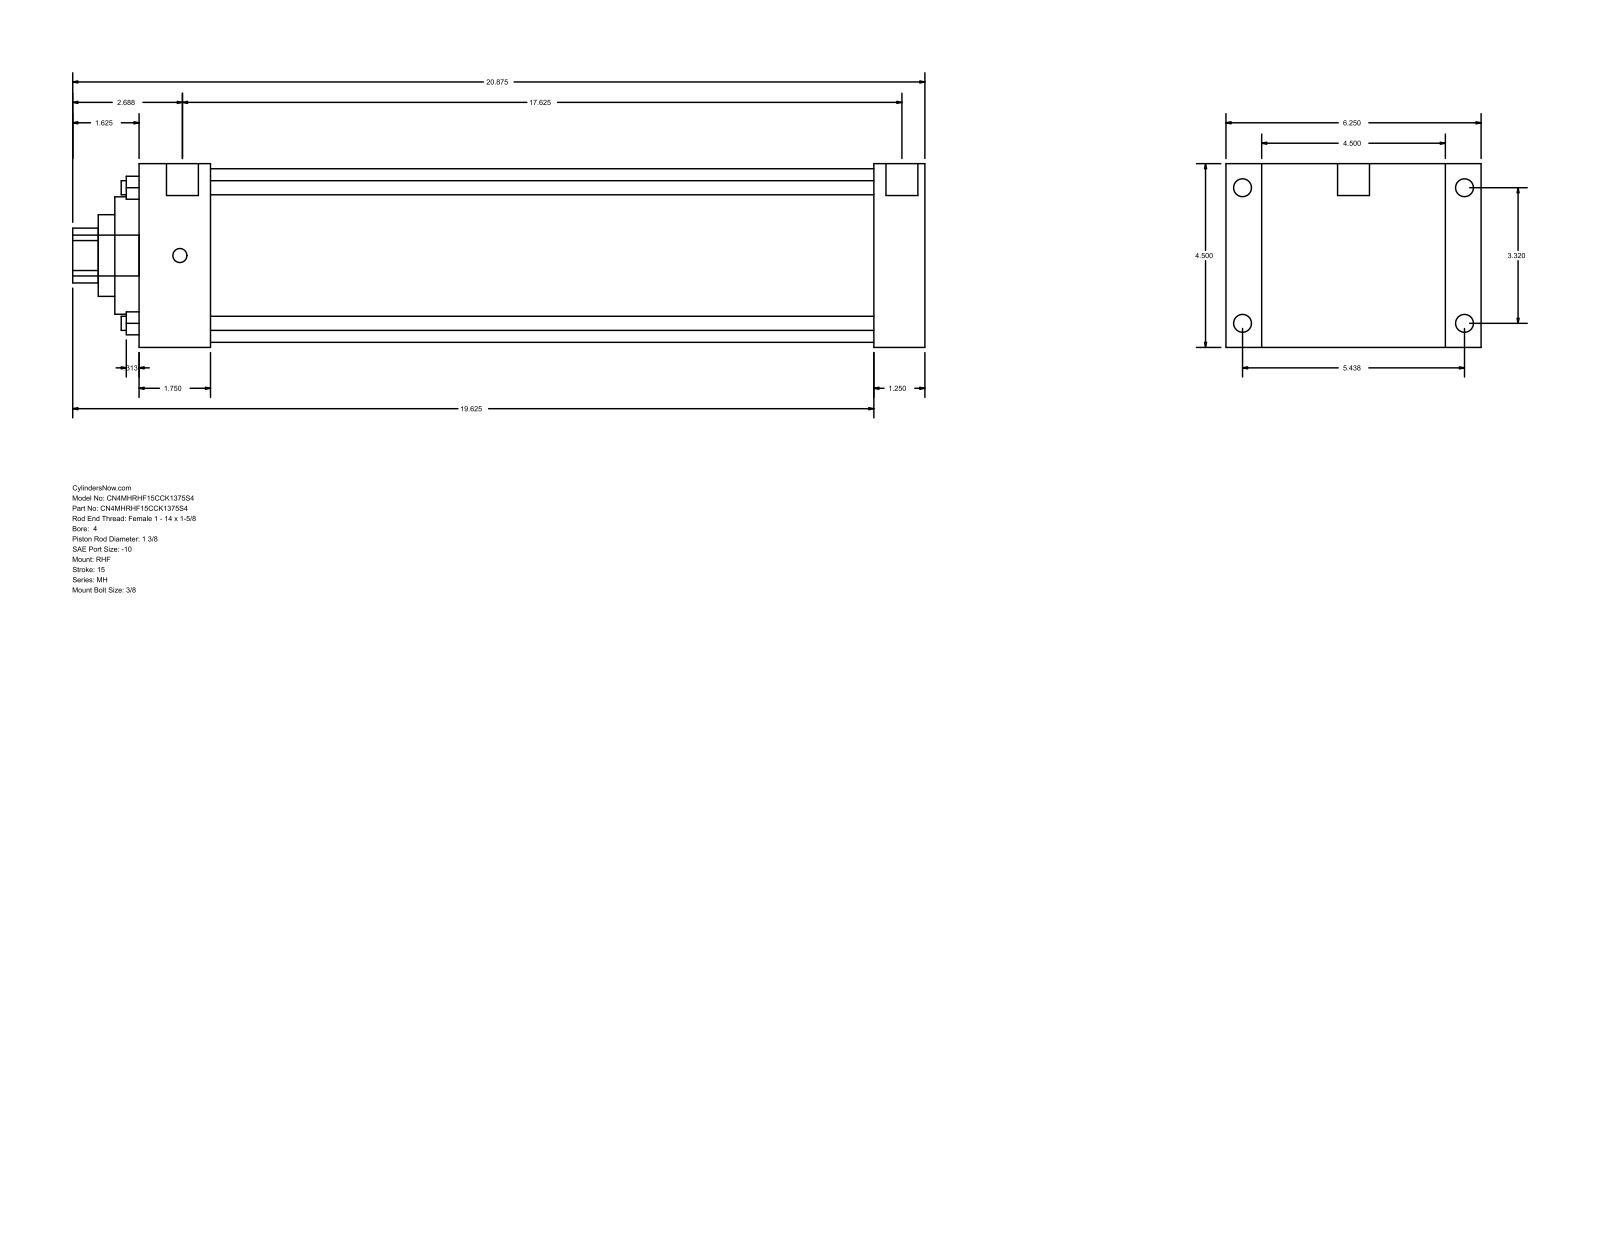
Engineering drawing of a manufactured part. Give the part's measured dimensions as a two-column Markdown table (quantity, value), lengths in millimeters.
| quantity | value |
| --- | --- |
| part name | MH_RHF__0400_1.375 |
| STEP written by | GSSL Pune (CONFIG_CONTROL_DESIGN) |
| units | millimeters |
| bodies | 0 solids, 90 faces (61 planar, 29 cylindrical, 0 other) |
| overall size | 530.23 × 158.75 × 114.3 |
| round holes (diameter × count) | 8.76 × 4, 34.92 × 1, 50.8 × 1, 73.03 × 1, 107.95 × 1 |
| round bosses / shafts (diameter × count) | 11.13 × 4, 8.73 × 4, 19.84 × 2, 25.4 × 1 |
| partial cylindrical surfaces (radius × count) | 17.06 × 1 |
| main face-to-face distances | 114.3, 488.96, 457.21, 31.75, 22.23, 136.53, 44.45, 412.76, 444.51, 158.76 |
| hole center spacings | 59.62, 84.32, 119.25 |
